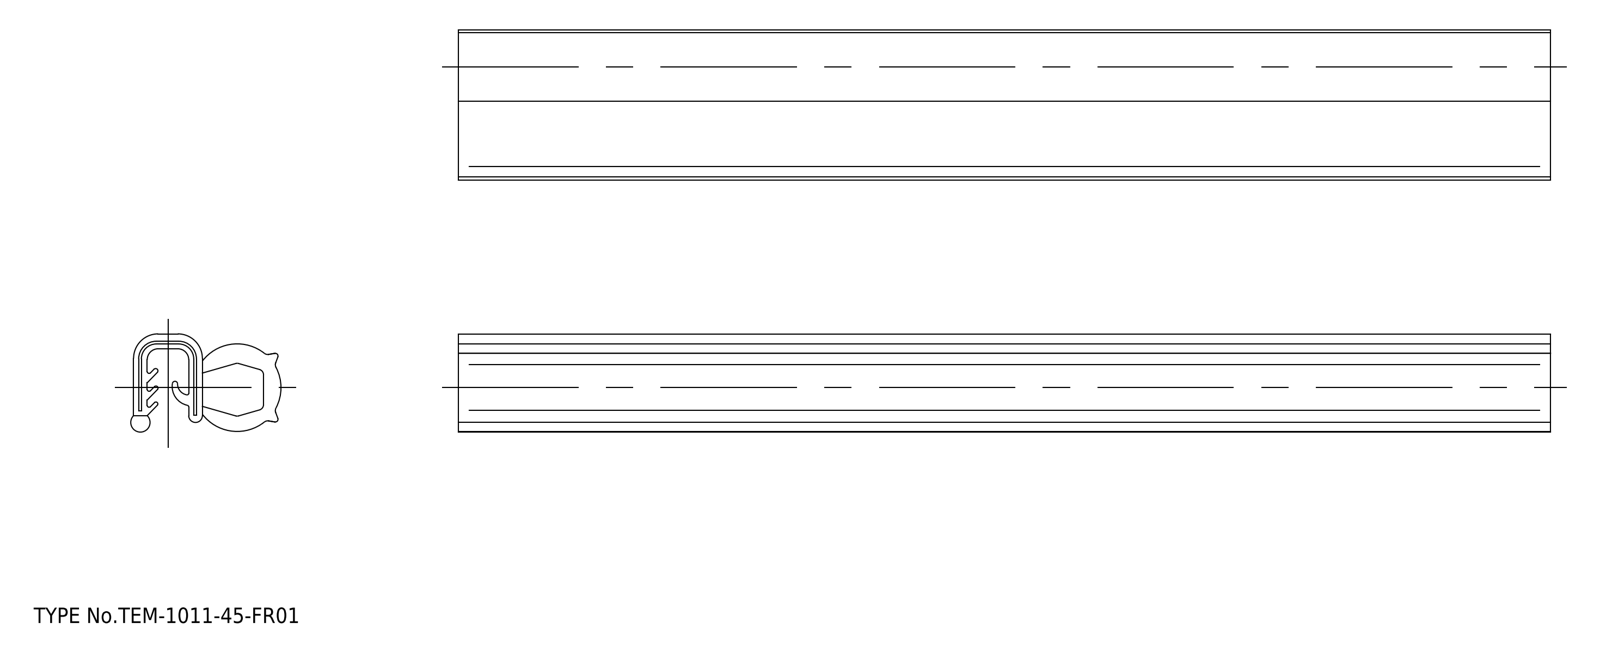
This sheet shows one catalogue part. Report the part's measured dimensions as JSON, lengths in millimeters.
{"part_name": "rubber foam; gasket; center core", "step_written_by": "spGate 17.5.1 (AUTOMOTIVE_DESIGN)", "units": "millimeters", "bodies": {"solids": 3, "faces": 91, "planar": 51, "cylindrical": 40, "other": 0}, "overall_size": [200, 27.52, 18], "volume_mm3": 43700, "surface_area_mm2": 62930, "partial_cylinders_radius": [[1, 6], [0.35, 3], [0.3, 2], [0.5, 2], [0.99, 2], [1, 2], [2, 2], [2.75, 2]], "face_to_face_distances": [0.5, 10.09, 10.59, 9.59, 11.67, 11.17, 1.58, 1.08, 2.5, 10.1]}
